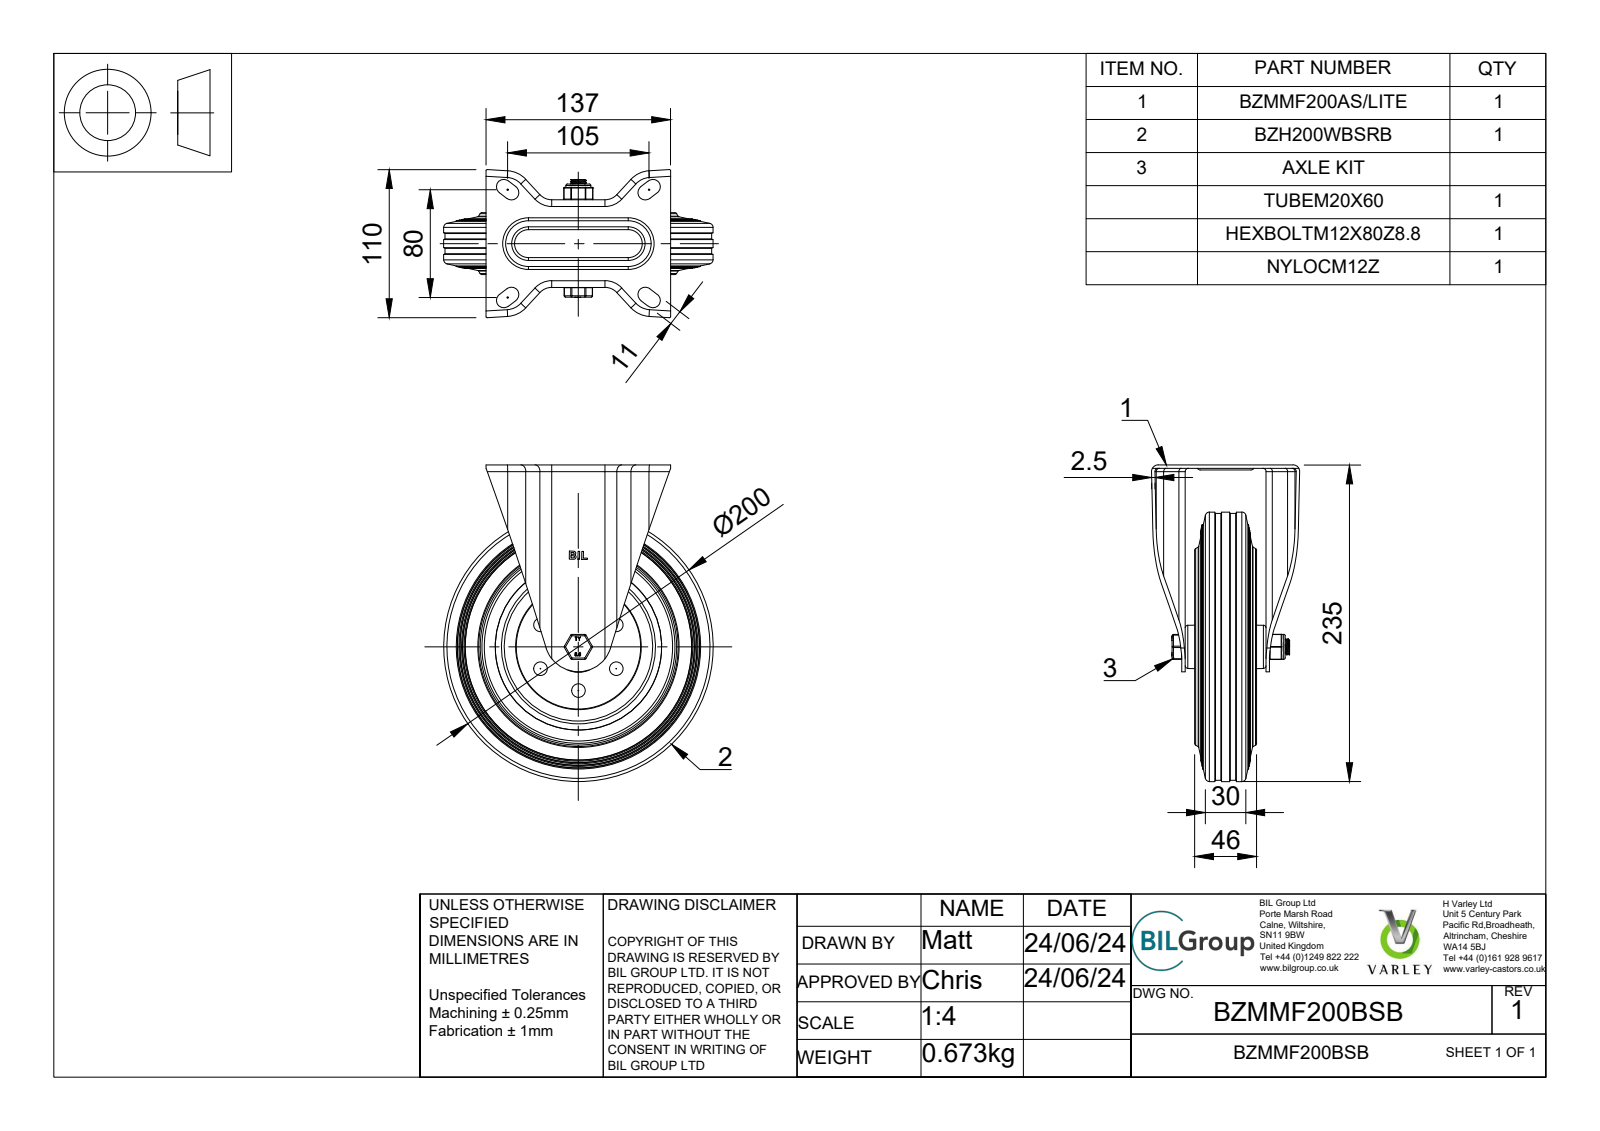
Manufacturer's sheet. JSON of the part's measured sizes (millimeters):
{"part_name": "BZMMF200BSB v4; BZMMF200AS/LITE v4; ZINC PLATED, PRESSED STEELM BRACKET; BZH200WBSRB v1 (+7 more)", "step_written_by": "Autodesk Translation Framework v13.14.0.145 (AUTOMOTIVE_DESIGN)", "units": "millimeters", "bodies": {"solids": 24, "faces": 661, "planar": 241, "cylindrical": 198, "other": 222}, "overall_size": [235, 200, 109.89], "volume_mm3": 1020000, "surface_area_mm2": 255009, "round_holes": [[5, 6], [12, 1], [12.25, 1], [12.5, 1], [14, 1], [20.2, 1], [21, 1], [30, 1], [95.68, 1], [123.5, 1]], "round_bosses_or_shafts": [[5, 10], [200, 1], [198, 1], [28, 1], [19.9, 1], [18.5, 1], [18, 1], [11.83, 1]], "partial_cylinders_radius": [[0.5, 18], [2.5, 18], [1, 12], [5, 10], [5.5, 8], [12, 4], [14.5, 4], [17.5, 4]], "face_to_face_distances": [2.5, 31.5, 62.5, 33.5, 29, 31, 2, 60, 5.04, 65], "hole_center_spacings": [32.5, 56.29, 56.3, 65.01, 65]}
